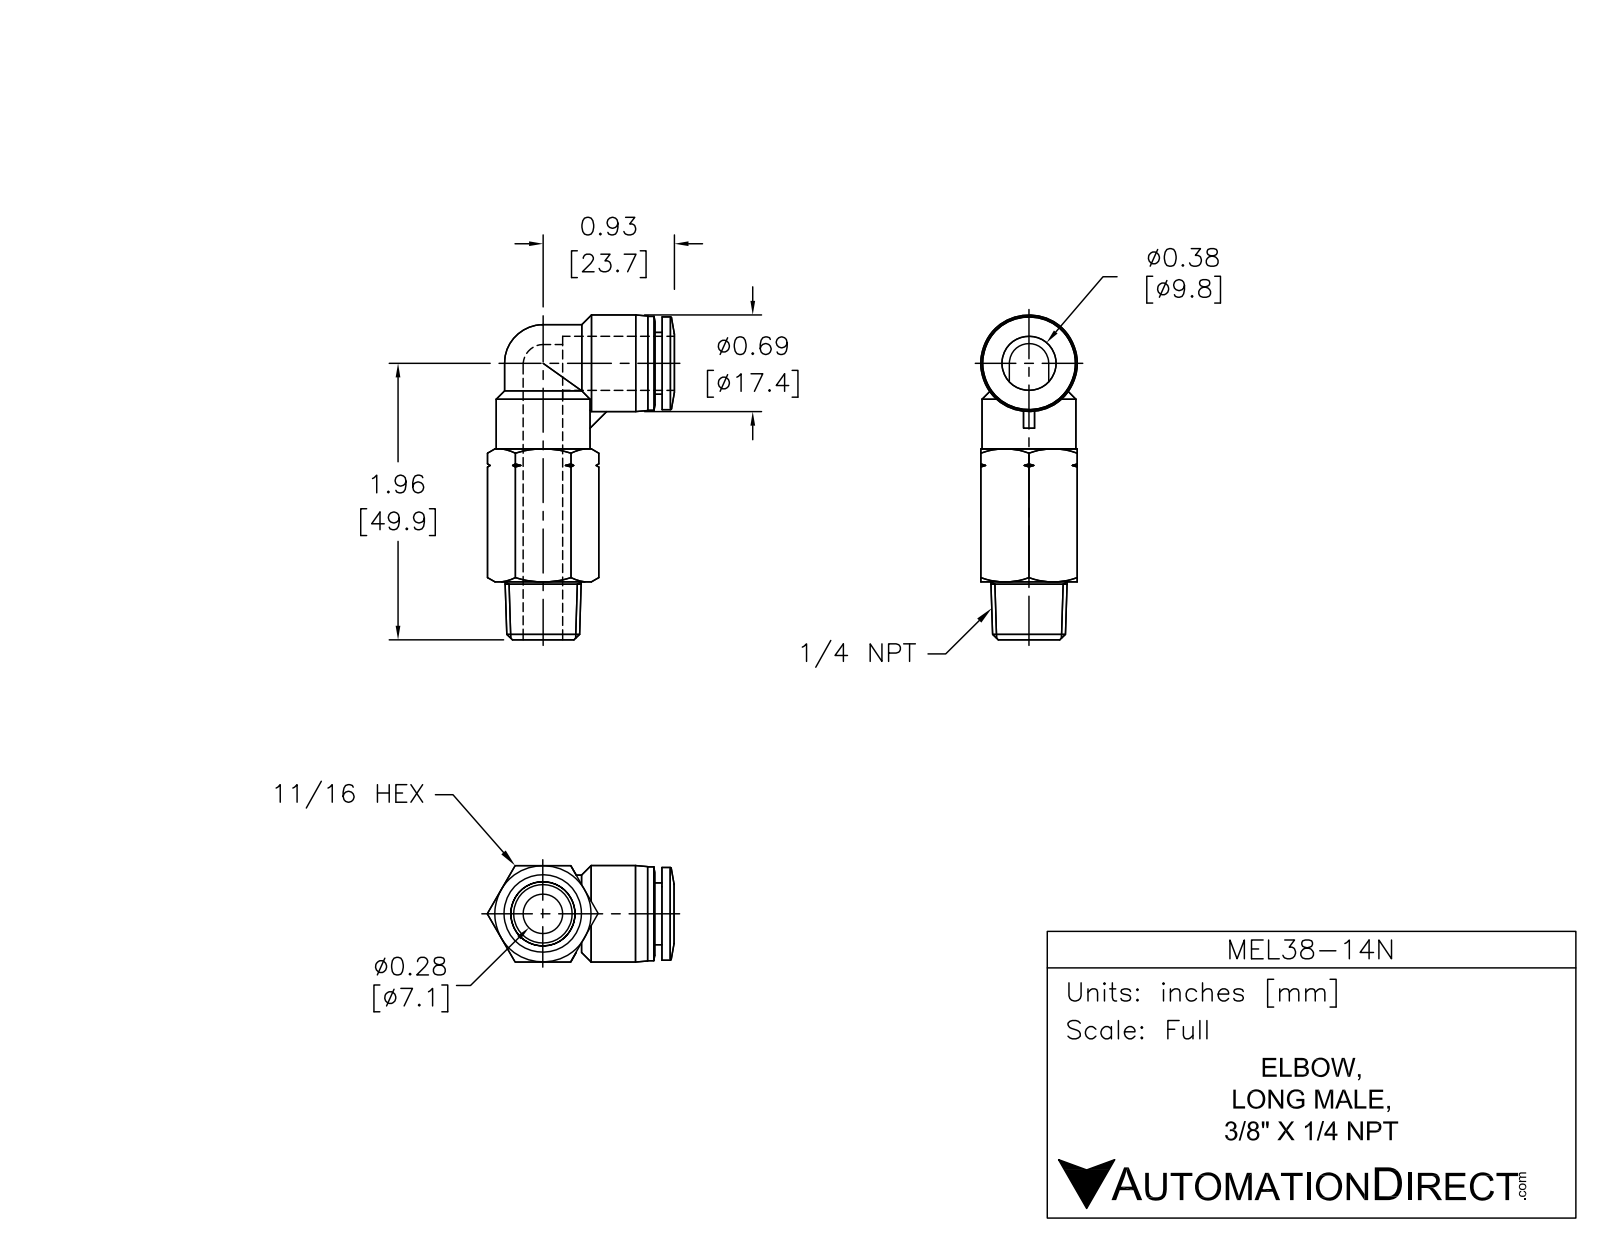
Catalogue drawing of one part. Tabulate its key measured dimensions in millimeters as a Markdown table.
| quantity | value |
| --- | --- |
| part name | MEL38-14N |
| STEP written by | SolidWorks 2015 (AUTOMOTIVE_DESIGN) |
| units | millimeters |
| bodies | 1 solid, 87 faces (16 planar, 20 cylindrical, 51 other) |
| overall size | 58.8 × 34.6 × 17.5 |
| volume | 12 100 mm³ |
| surface area | 6 295 mm² |
| round holes (diameter × count) | 7 × 2, 9.8 × 1 |
| round bosses / shafts (diameter × count) | 17 × 2, 17.5 × 1, 16.8 × 1, 14 × 1, 11.2 × 1 |
| partial cylindrical surfaces (radius × count) | 7 × 1 |
| main face-to-face distances | 17.4, 1.3, 10.5, 16.6, 17.9, 34.5, 24, 7.7, 9.7, 2 |
